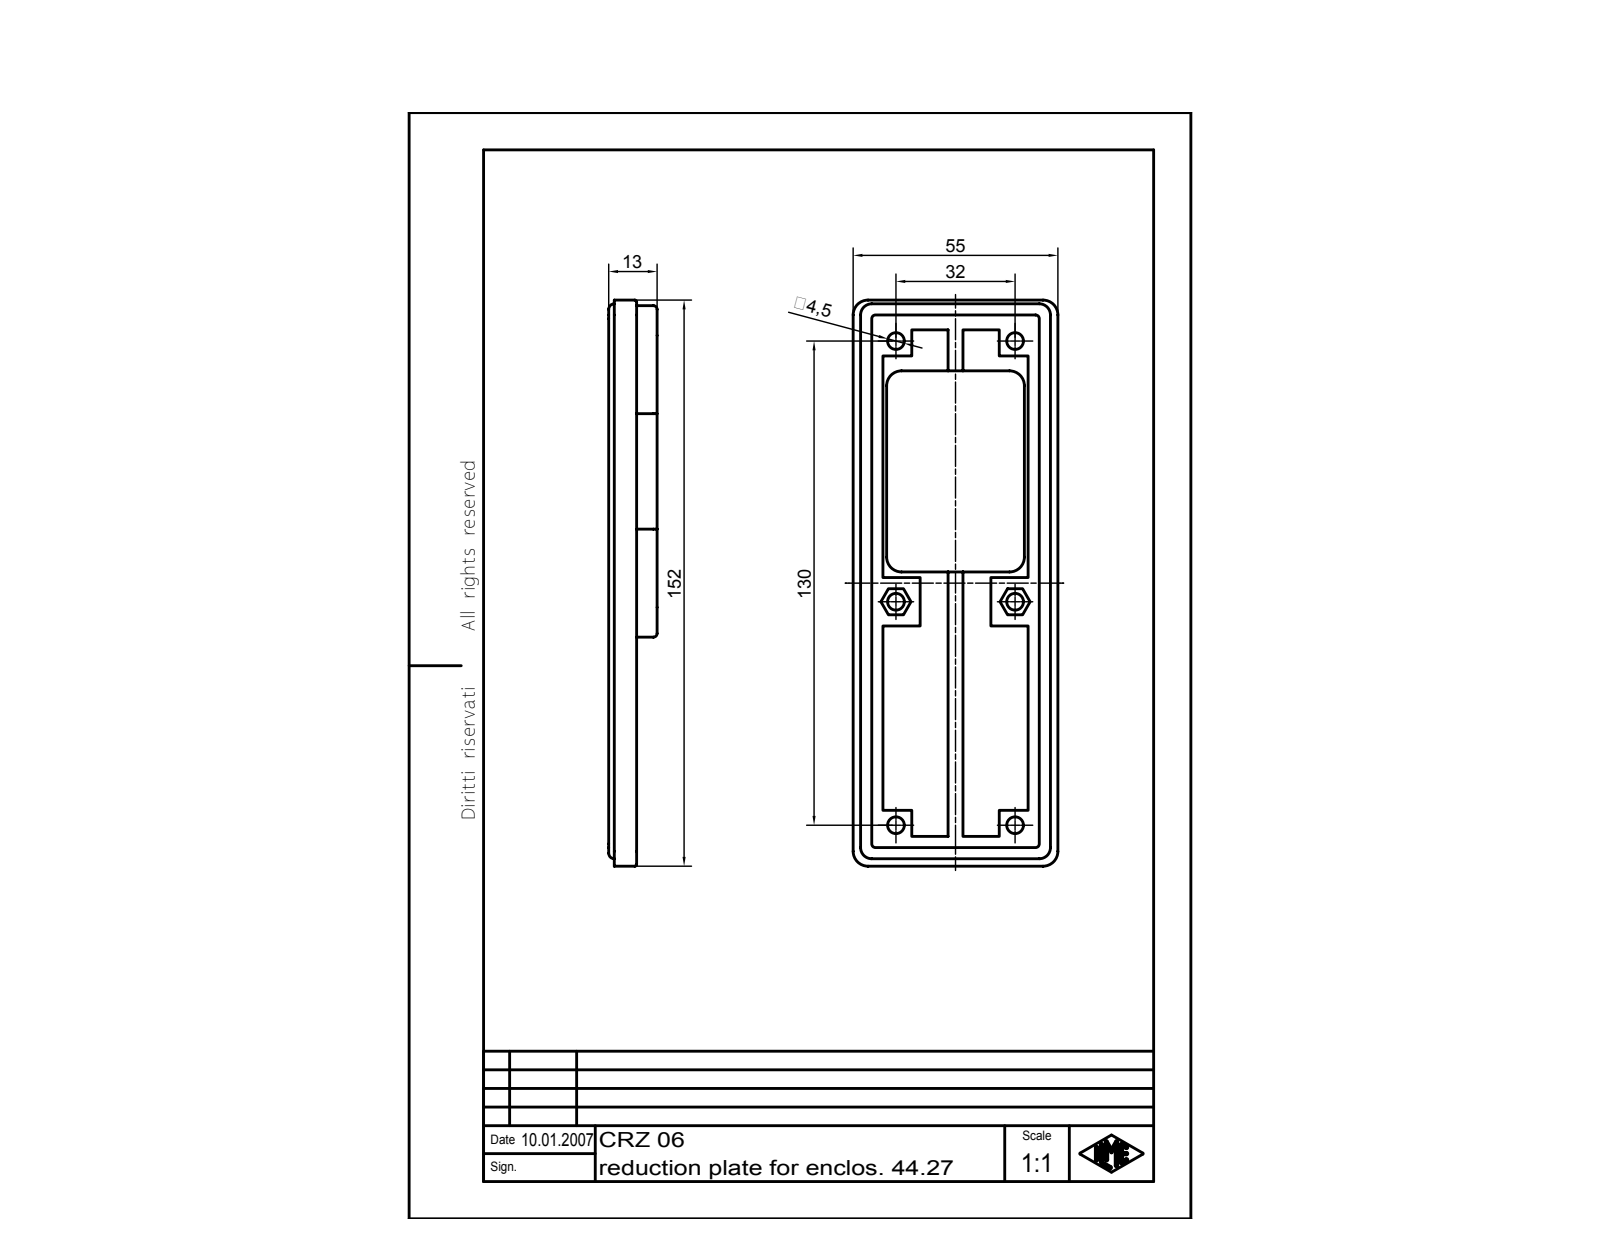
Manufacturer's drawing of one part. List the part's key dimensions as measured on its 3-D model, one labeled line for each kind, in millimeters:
Part name (STEP PRODUCT): CRZ 06
STEP written by: Autodesk Inventor 7 (AUTOMOTIVE_DESIGN)
Units: millimetres
Bodies: 1 solid, 209 faces (107 planar, 82 cylindrical, 20 other)
Overall size (bounding box): 152 × 55 × 13
Volume: 34 883 mm³ · Surface area: 20 646 mm²
Round holes (diameter × count): ⌀4.5 ×6
Partial cylindrical surfaces — rounded edges, fillets, slot ends (radius × count): R0.1 ×14, R1 ×8, R4 ×8, R0.5 ×4, R1.5 ×4, R5 ×4, R8 ×4
Main face-to-face distances: 3, 6, 55, 8, 17.5, 47, 1.75, 4.75, 50.25, 53.25
Hole centre spacings: 32, 60, 68, 70, 76.97, 130, 133.88
